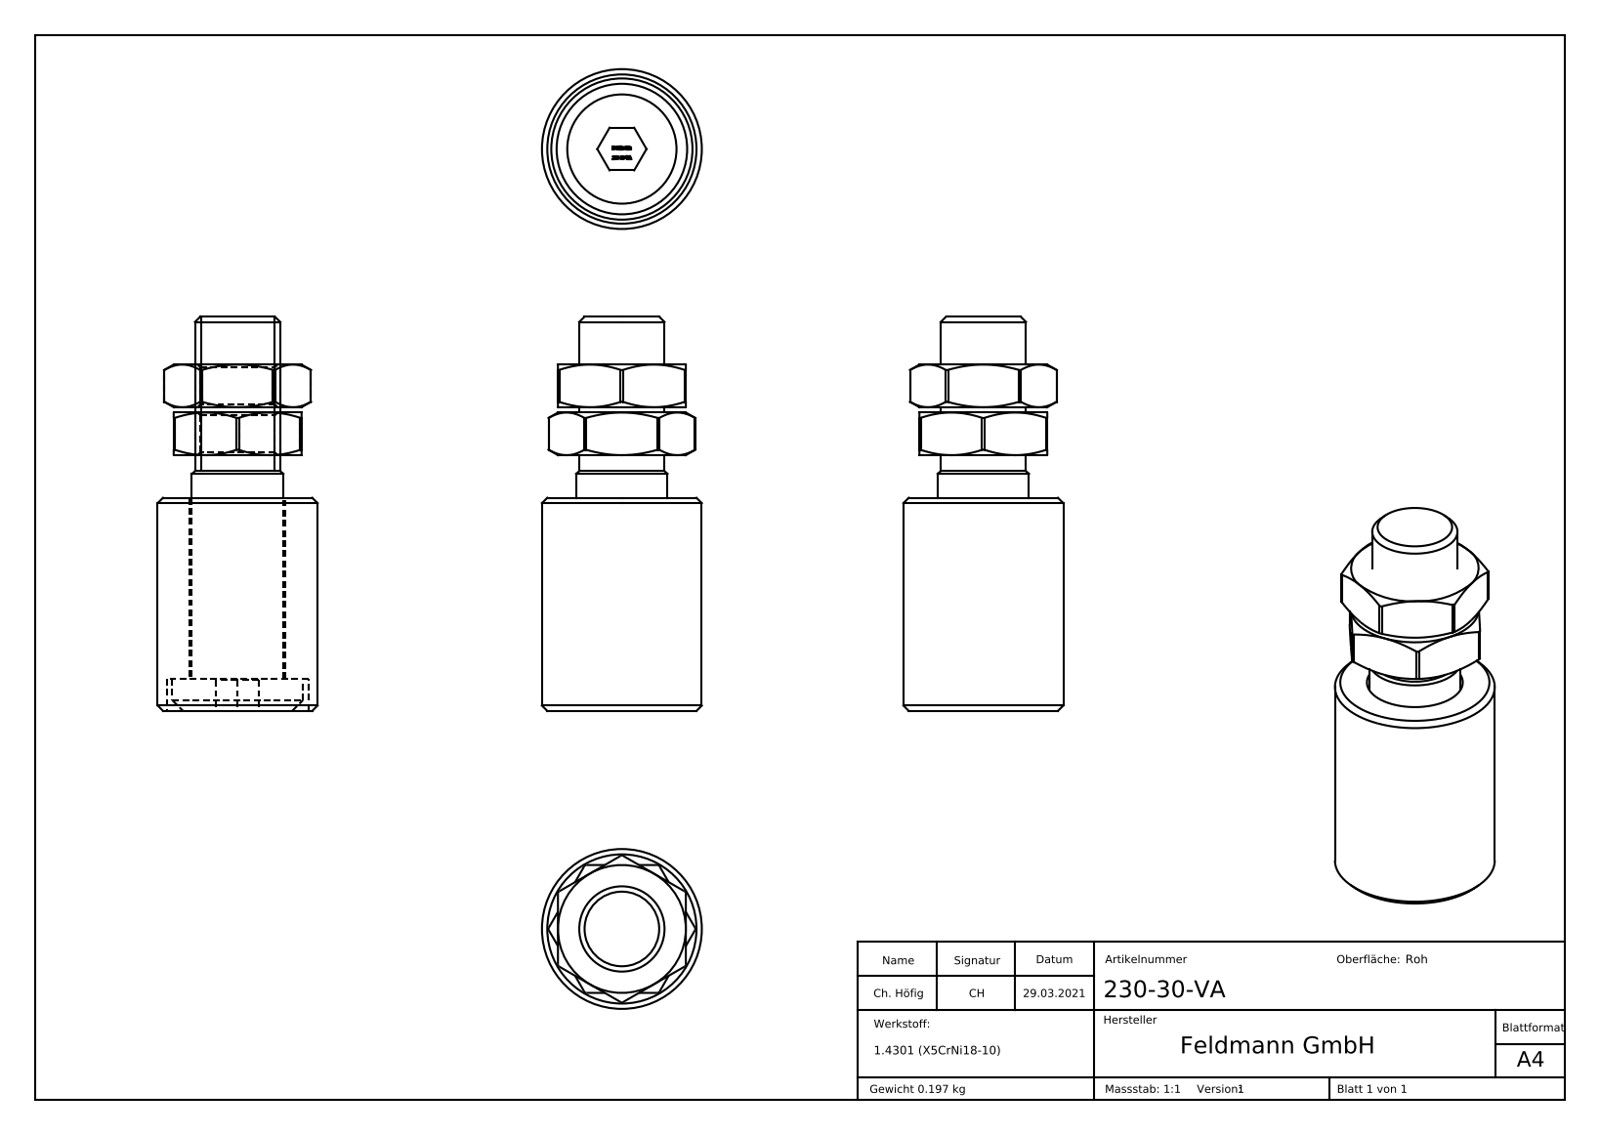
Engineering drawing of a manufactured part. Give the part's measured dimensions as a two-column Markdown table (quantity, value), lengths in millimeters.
| quantity | value |
| --- | --- |
| part name | 230-xx-VA Teil1_230-30-VA Teil1; 230-xx-VA Teil1; DIN 439 M4-M20_DIN 439 M16; 230-30-VA (+3 more) |
| STEP written by | SolidWorks 2018 (CONFIG_CONTROL_DESIGN) |
| units | millimeters |
| bodies | 4 solids, 318 faces (144 planar, 28 cylindrical, 146 other) |
| overall size | 22000 × 14000 × 14000 |
| volume | 38 825 mm³ |
| surface area | 15 234 mm² |
| round holes (diameter × count) | 14 × 1, 18 × 1, 26.5 × 1 |
| round bosses / shafts (diameter × count) | 30 × 1, 24.5 × 1, 17.15 × 1, 16 × 1 |
| partial cylindrical surfaces (radius × count) | 0.5 × 12 |
| main face-to-face distances | 8, 17, 9, 24, 34, 16, 6, 40, 1, 48 |
